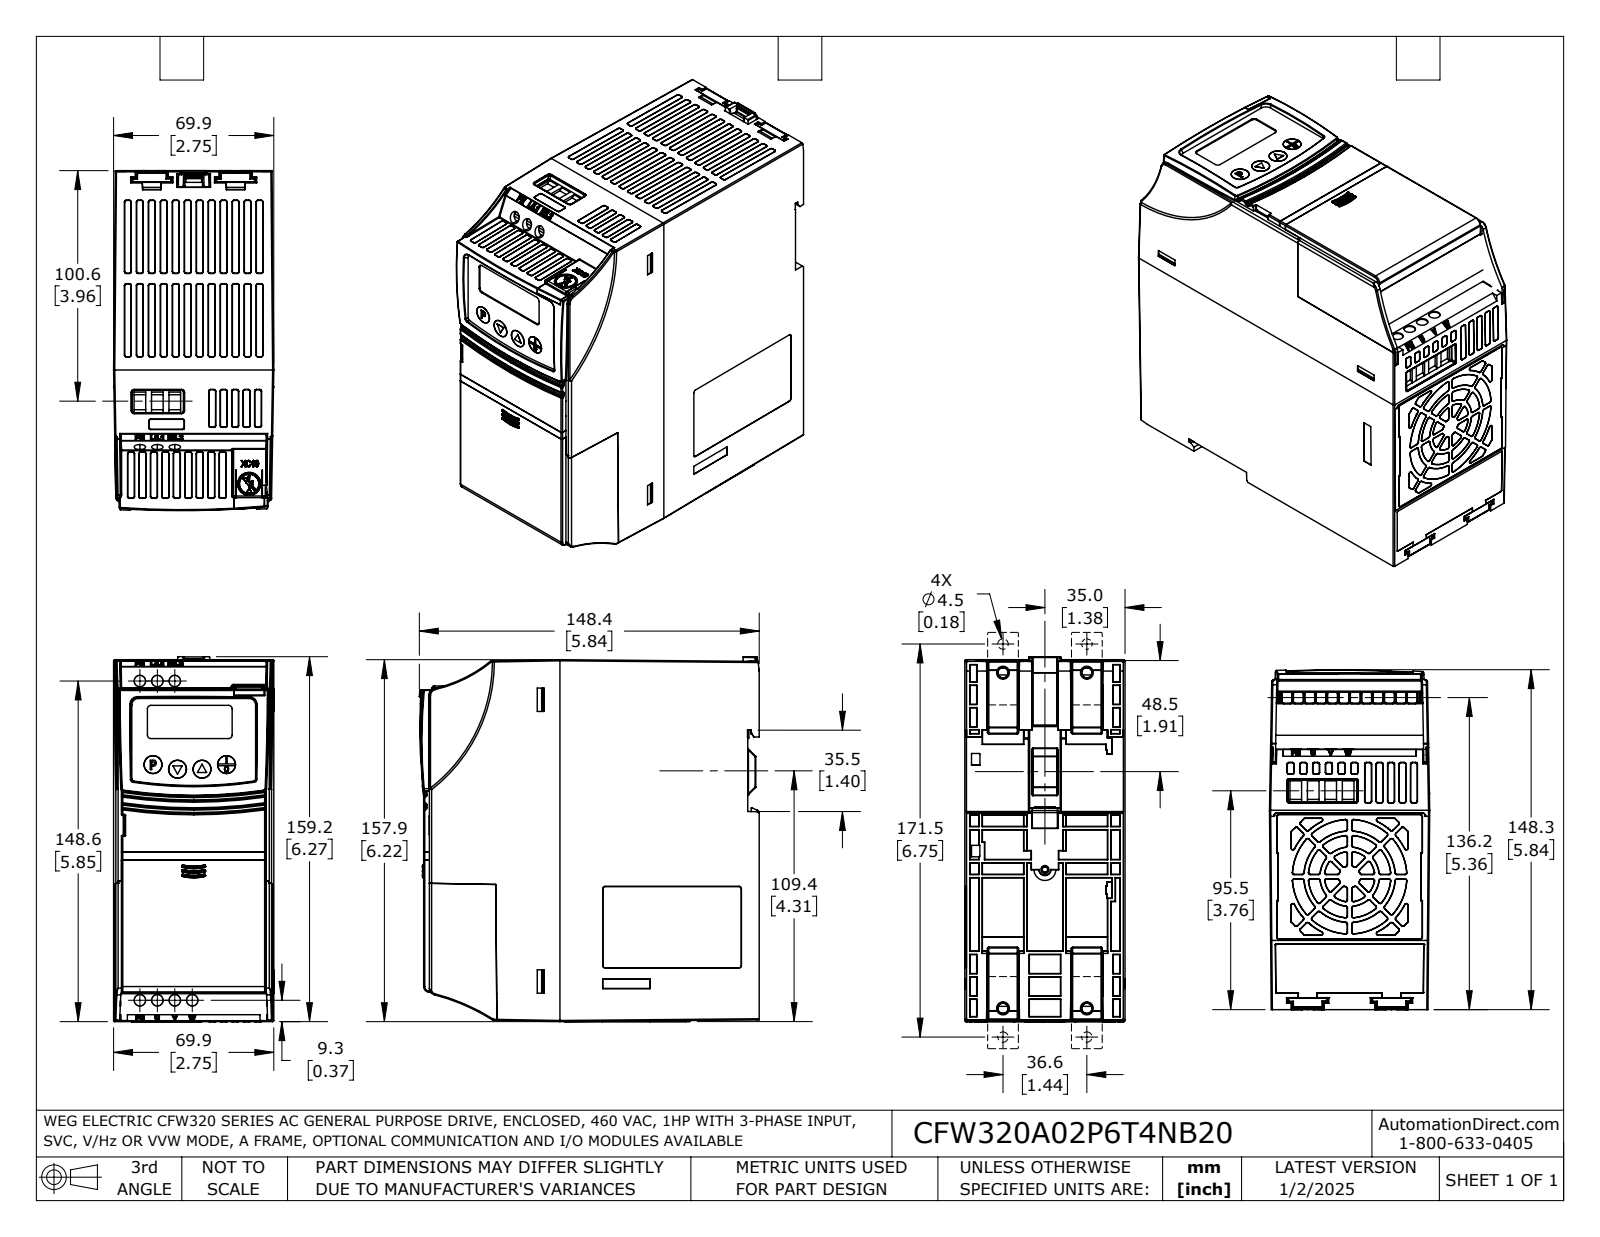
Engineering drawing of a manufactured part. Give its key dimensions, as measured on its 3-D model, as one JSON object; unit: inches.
{"part_name": "CFW320A02P6T4NB20", "step_written_by": "SolidWorks 2021 (AUTOMOTIVE_DESIGN)", "units": "inches", "bodies": {"solids": 6, "faces": 3715, "planar": 1587, "cylindrical": 853, "other": 1275}, "overall_size": [6.269, 5.841, 2.754], "volume_in3": 15.24, "surface_area_in2": 309, "round_holes": [[0.197, 3]], "partial_cylinders_radius": [[0.012, 327], [0.02, 150], [0.039, 13], [0.03, 5], [0.118, 3], [0.01, 2], [0.098, 1], [0.126, 1]], "face_to_face_distances": [0.07, 0.055, 0.019, 0.05, 6, 5.33, 5.275, 5.571, 5.516, 0.241], "hole_center_spacings": [0.3, 0.6]}
